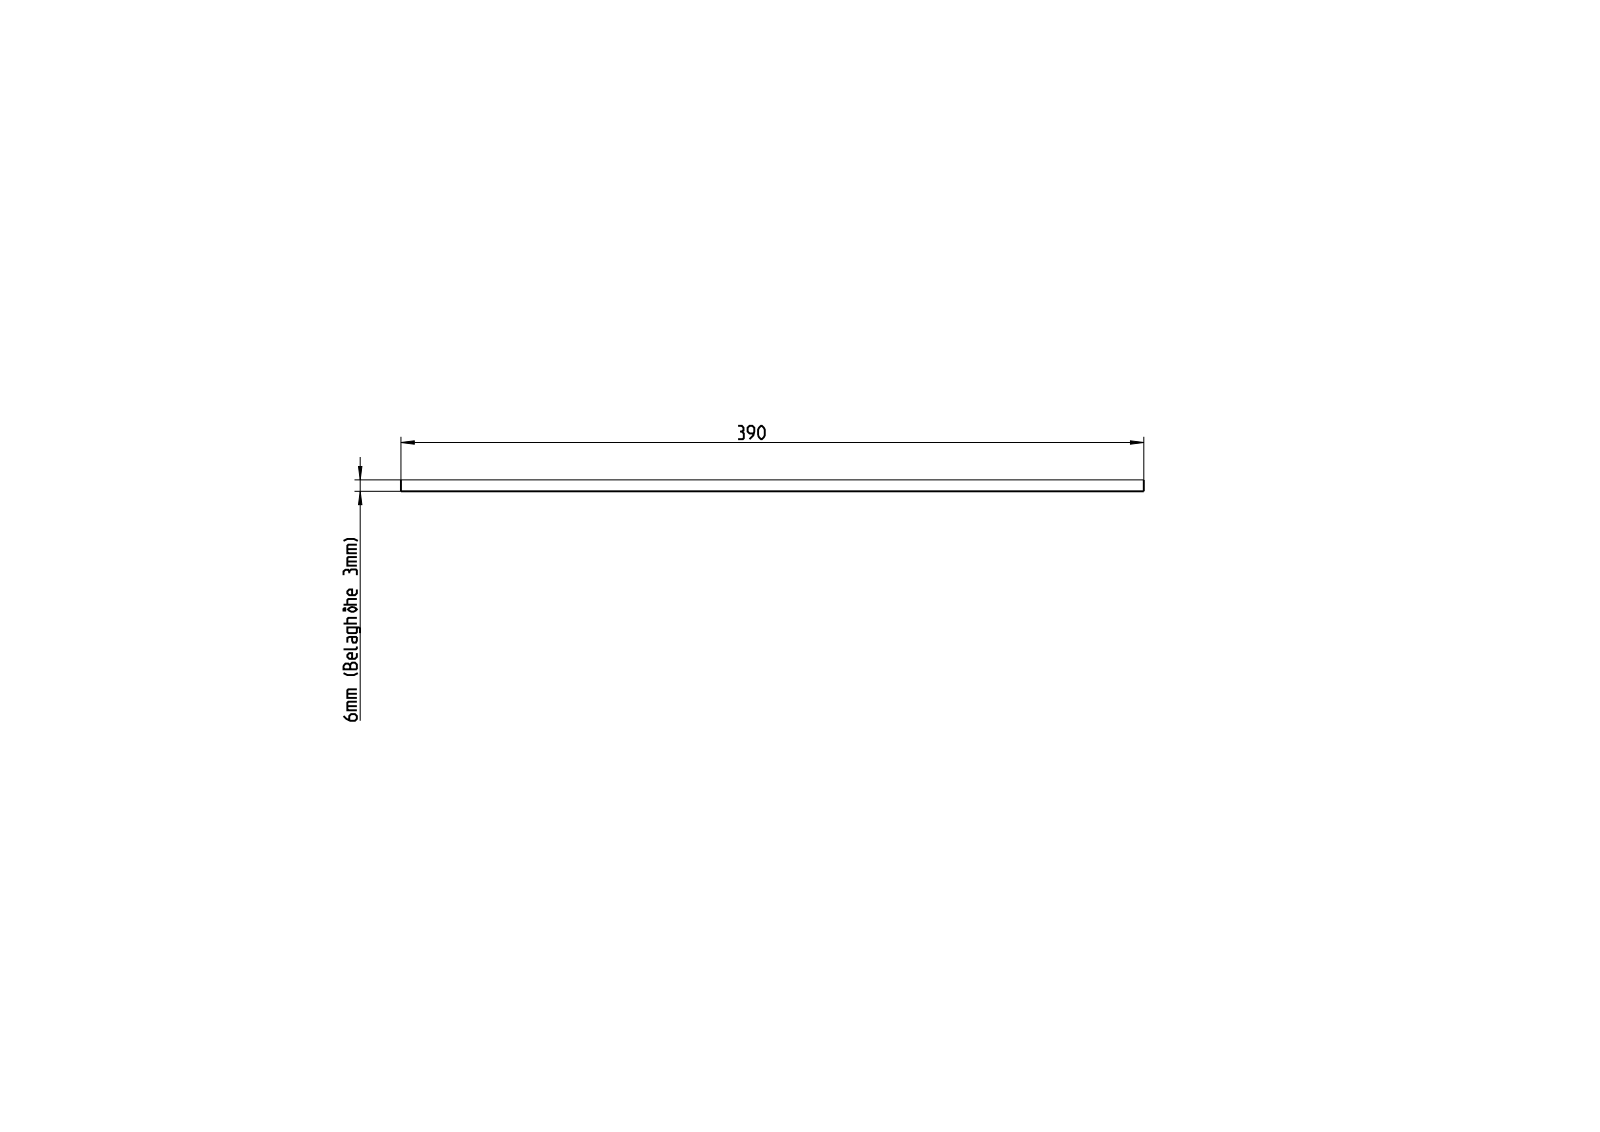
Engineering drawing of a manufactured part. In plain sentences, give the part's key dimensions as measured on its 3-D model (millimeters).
The part is named "BKG4002W3; BKG4002W3_ASM". Its 3-D file was written by "CREO PARAMETRIC BY PTC INC, 2022024 (AUTOMOTIVE_DESIGN)". It is 1 solid with 6 faces: 6 planar, 0 cylindrical and 0 other. Overall it measures 999 by 390 by 6 millimeters. Its volume is 2 338 000 cubic millimeters and its surface area 795 888 square millimeters. The main face-to-face distances are 6, 390, 999.
